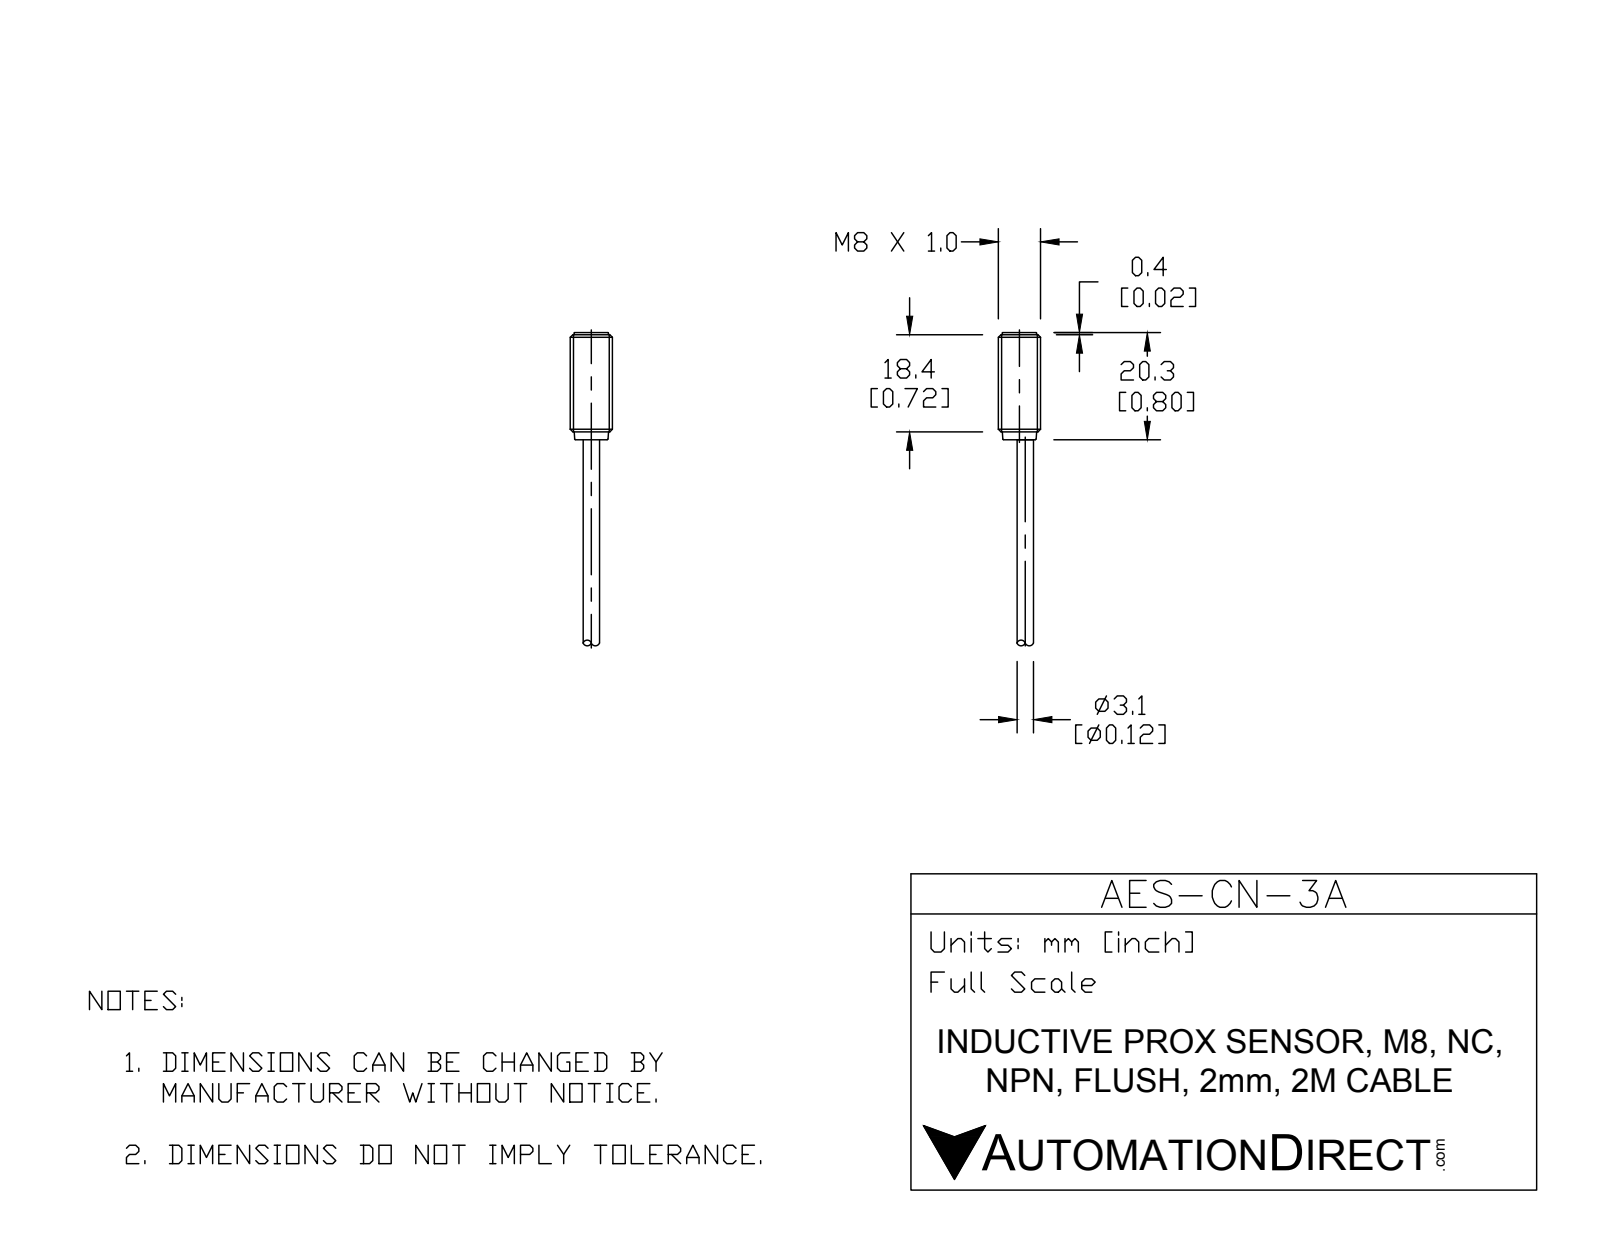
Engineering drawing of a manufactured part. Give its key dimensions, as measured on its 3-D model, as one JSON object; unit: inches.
{"part_name": "AES-CN-3A", "step_written_by": "SolidWorks 2015 (CONFIG_CONTROL_DESIGN)", "units": "inches", "bodies": {"solids": 1, "faces": 21, "planar": 5, "cylindrical": 6, "other": 10}, "overall_size": [2.752, 0.315, 0.315], "volume_in3": 0.081, "surface_area_in2": 1.634, "round_bosses_or_shafts": [[0.315, 1], [0.256, 1], [0.122, 1]], "face_to_face_distances": [0.783, 1.969, 2.752, 2.736, 0.768, 0.016, 2.028, 0.059, 0.709, 0.724]}
